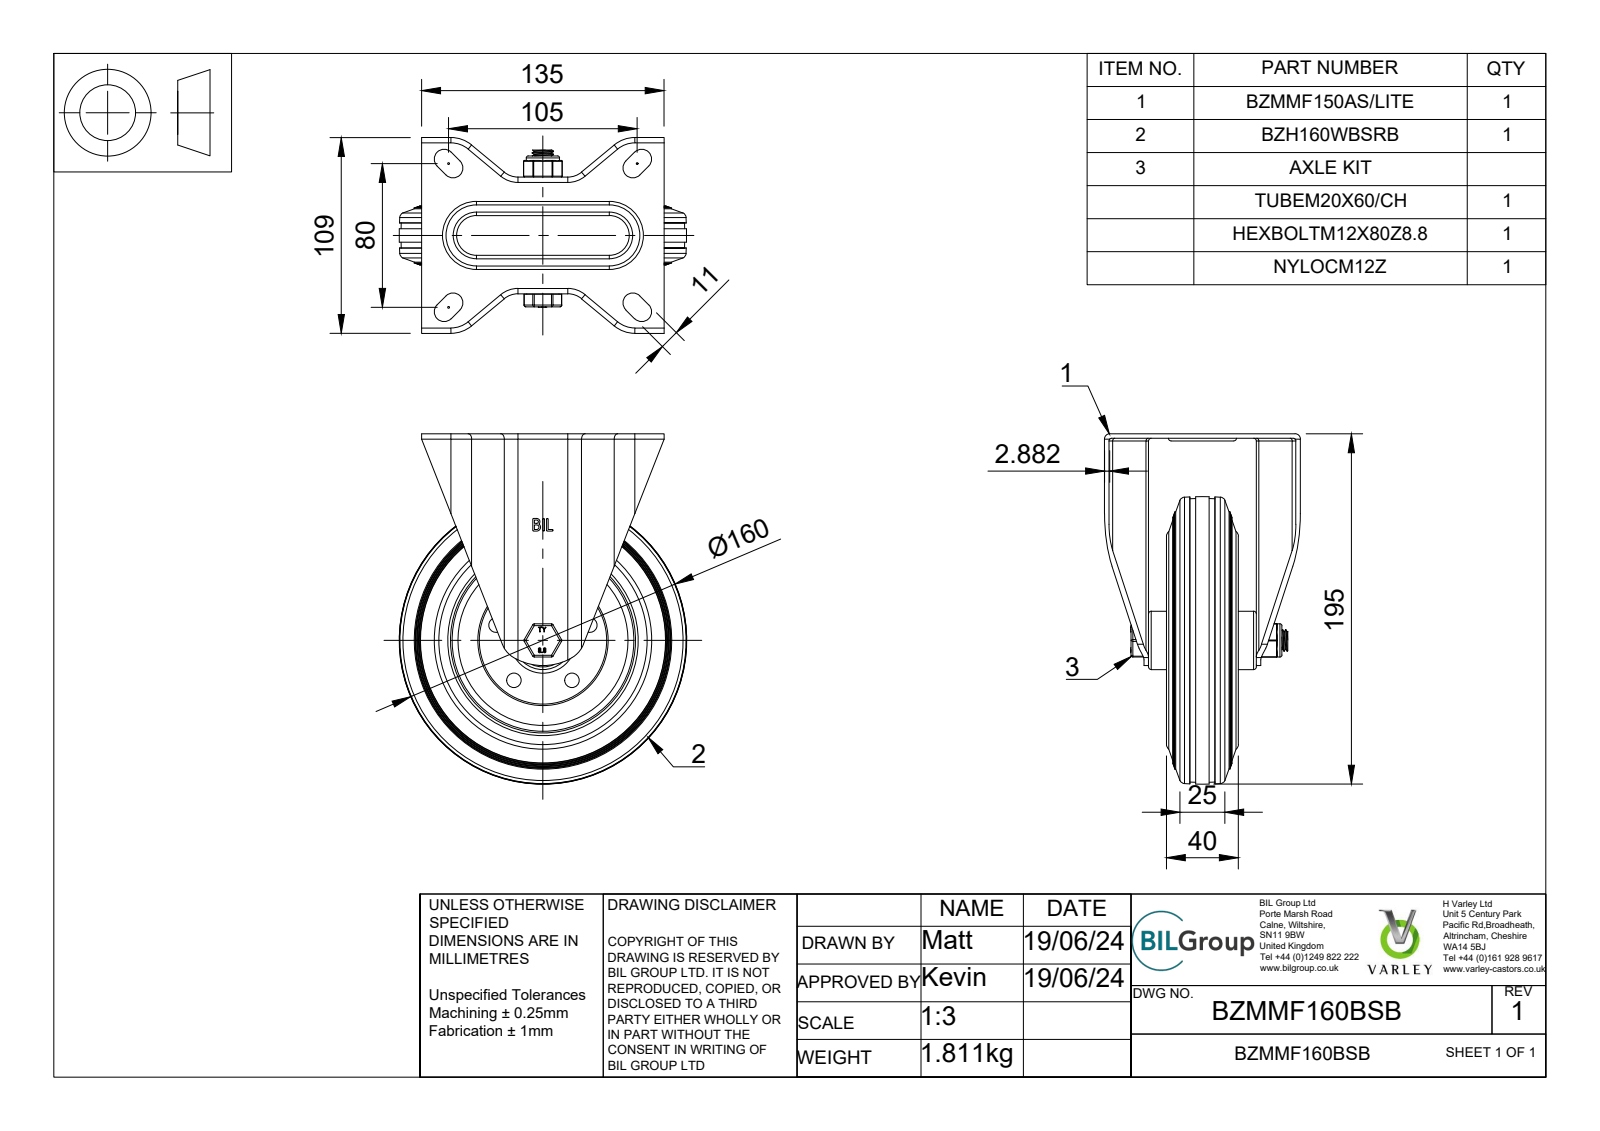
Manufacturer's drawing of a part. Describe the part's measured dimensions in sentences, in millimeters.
The part is named "BZMMF160BSB v3; BZMMF150ASLITE v1; ZINC PLATED, PRESSED STEEL BRACKET; BZH160WBSRB v1 (+7 more)". Its 3-D file was written by "Autodesk Translation Framework v13.14.0.145 (AUTOMOTIVE_DESIGN)". It is 24 solids with 603 faces: 238 planar, 204 cylindrical and 161 other. Overall it measures 195 by 160 by 109 millimeters. Its volume is 633 726 cubic millimeters and its surface area 212 037 square millimeters. Round holes: 5 of diameter 6, 1 of diameter 12, 1 of diameter 12.25, 1 of diameter 12.5, 1 of diameter 14, 1 of diameter 20, 1 of diameter 29.5. Round bosses or shafts: 10 of diameter 4.5, 5 of diameter 8, 1 of diameter 103, 1 of diameter 32.5, 1 of diameter 19.9, 1 of diameter 18.5, 1 of diameter 18, 1 of diameter 11.83. Partial cylindrical surfaces (rounded edges, fillets, slot ends): 18 of radius 0.5, 12 of radius 1, 12 of radius 1.5, 8 of radius 3, 8 of radius 5.5, 4 of radius 2, 4 of radius 6, 4 of radius 9. The main face-to-face distances are 2.5, 30, 24.24, 22, 32, 32.5, 62.5, 34.5, 30.5, 50. The hole center spacings are 32.3, 27.48, 52.26, 27.47, 52.27.
